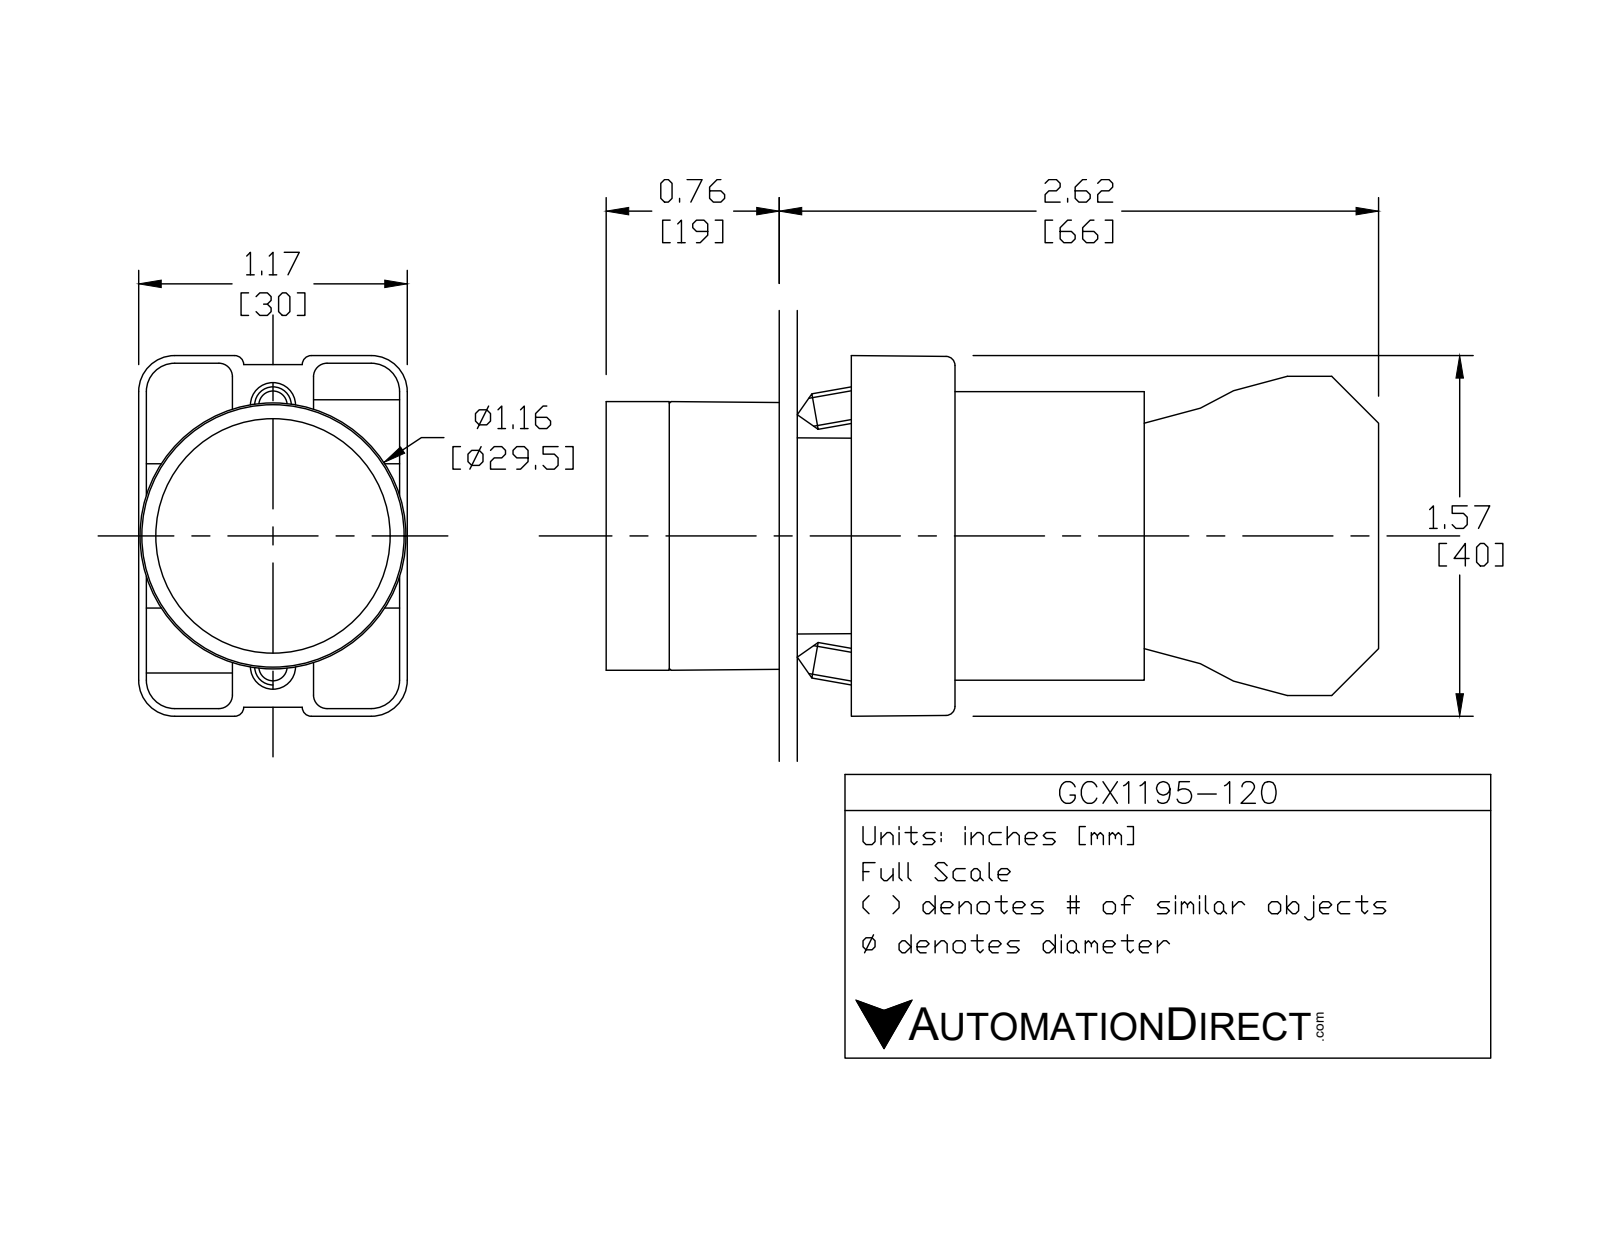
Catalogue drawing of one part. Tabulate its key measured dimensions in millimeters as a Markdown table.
| quantity | value |
| --- | --- |
| part name | ecx1040; ecx1029; GCX1195-120; ECX1050 (+1 more) |
| STEP written by | SolidWorks 2016 (AUTOMOTIVE_DESIGN) |
| units | millimeters |
| bodies | 8 solids, 431 faces (252 planar, 148 cylindrical, 31 other) |
| overall size | 84.3 × 40.2 × 29.9 |
| volume | 45 790 mm³ |
| surface area | 25 000 mm² |
| round holes (diameter × count) | 2 × 2, 3.1 × 2, 3.3 × 2, 2.2 × 1, 5 × 1, 11.9 × 1, 22.3 × 1, 22.6 × 1, 26 × 1 |
| round bosses / shafts (diameter × count) | 4 × 4, 29.8 × 1, 25.5 × 1, 24 × 1, 21.7 × 1, 19.8 × 1, 12.8 × 1 |
| partial cylindrical surfaces (radius × count) | 1.5 × 24, 1 × 12, 3.1 × 12, 4 × 12, 1 × 8, 3.3 × 2, 0.5 × 1, 1.6 × 1 |
| main face-to-face distances | 21, 51.3, 30.3, 14.7, 29.7, 0.8, 7, 0.8, 19, 14.6 |
| hole center spacings | 6, 13.8, 12, 12.4 |
